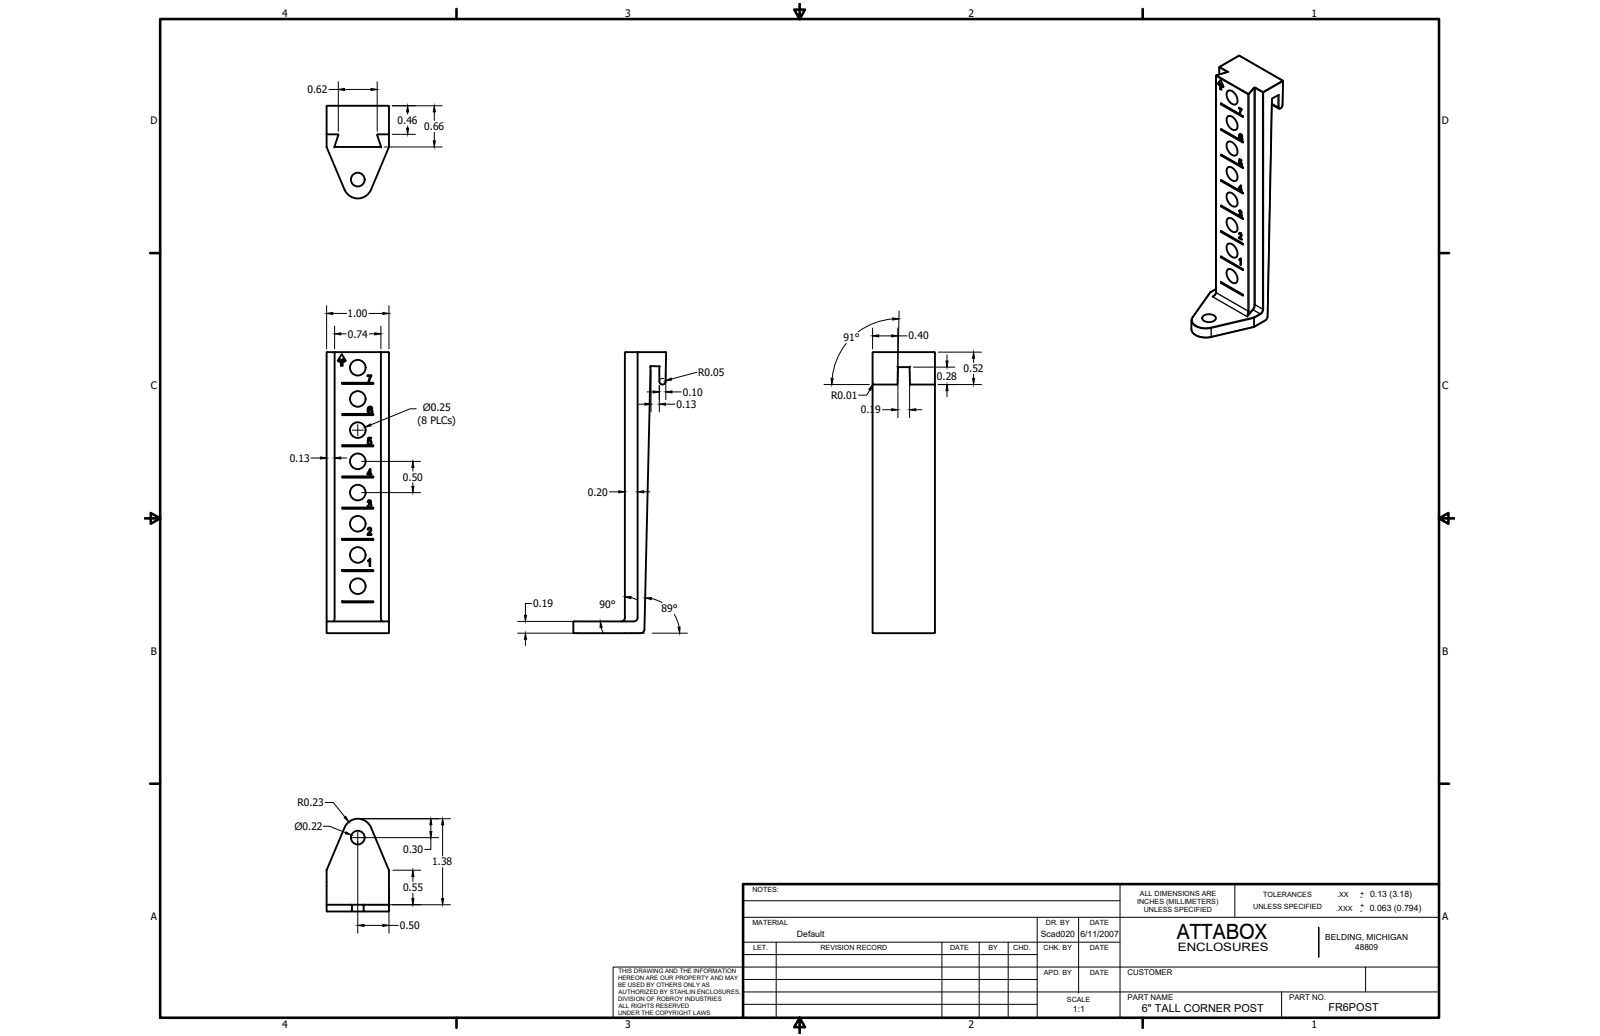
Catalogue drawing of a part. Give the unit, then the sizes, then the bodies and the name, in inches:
Units: inches
Overall size (bounding box): 10.622 × 8.622 × 4.703
Round holes (diameter × count): ⌀0.25 ×32, ⌀0.217 ×4, ⌀0.22 ×4
Round bosses / shafts (diameter × count): ⌀0.433 ×4, ⌀0.373 ×4, ⌀0.19 ×4
Partial cylindrical surfaces — rounded edges, fillets, slot ends (radius × count): R0.01 ×158, R0.06 ×16, R0.049 ×4, R0.23 ×4
Main face-to-face distances: 11.295, 4.441, 6.855, 5.44, 5.855, 1.415, 1, 0.203, 4.643, 5.643
Hole centre spacings: 1.5, 0.5, 1, 1.732, 2.061, 1.414, 2, 2.45
Volume: 5.842 in³ · Surface area: 75.79 in²
Bodies: 12 solids, 1132 faces (568 planar, 240 cylindrical, 324 other)
Part name (STEP PRODUCT): FR6POST
STEP written by: SolidWorks 2019 (AUTOMOTIVE_DESIGN)
